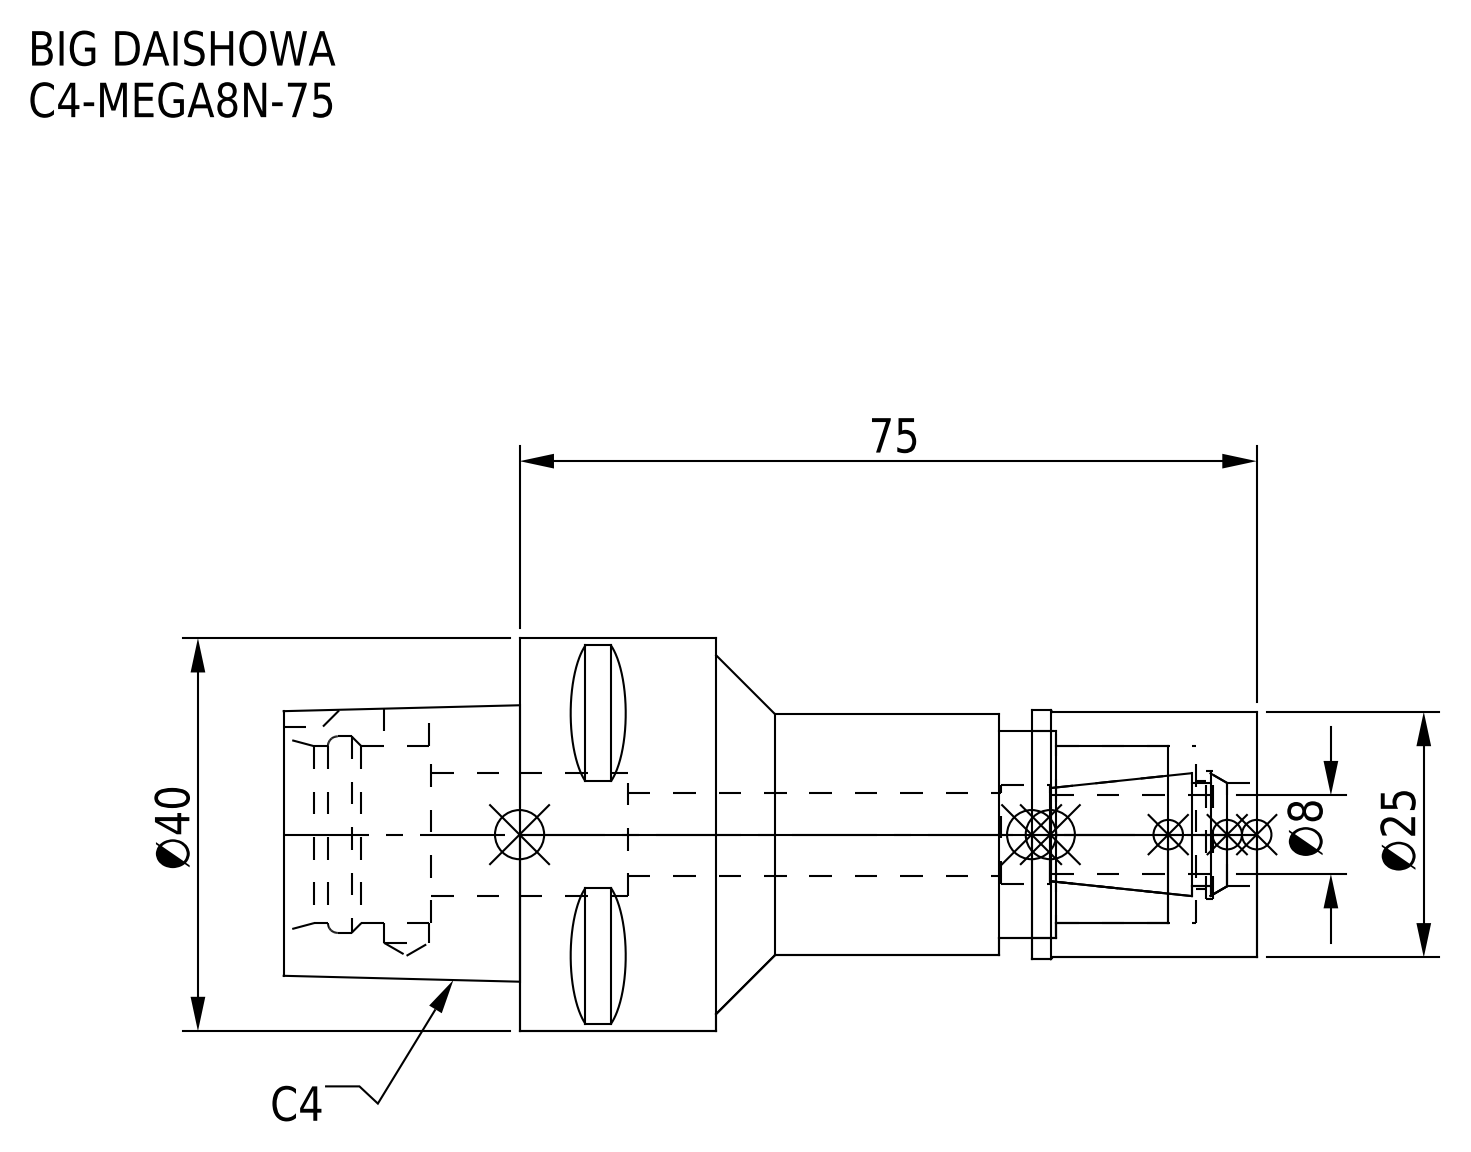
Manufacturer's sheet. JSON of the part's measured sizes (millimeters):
{"part_name": "DXF_TEMP_ASSY_ASM_4_ASM.stp; C4-MEGA8N-75-080.stp; C4-MEGA8N-75-080_ASM.stp; C4-MEGA8N-75-080-FreeParts (+3 more)", "step_written_by": "SolidWorks 2019 (CONFIG_CONTROL_DESIGN)", "units": "millimeters", "bodies": {"solids": 2, "faces": 95, "planar": 38, "cylindrical": 39, "other": 18}, "overall_size": [99, 40, 40], "volume_mm3": 54800, "surface_area_mm2": 17216, "round_holes": [[4.6, 1], [8.4, 1], [10, 1], [10.5, 1], [11, 1], [12.5, 1], [13, 1], [18, 1], [20, 1], [21, 1]], "round_bosses_or_shafts": [[40, 1], [25.3, 1], [25, 1], [24.5, 1]], "partial_cylinders_radius": [[3, 1]], "face_to_face_distances": [75, 20, 9, 48.8, 55, 57.8, 99, 44, 24, 20.4]}
